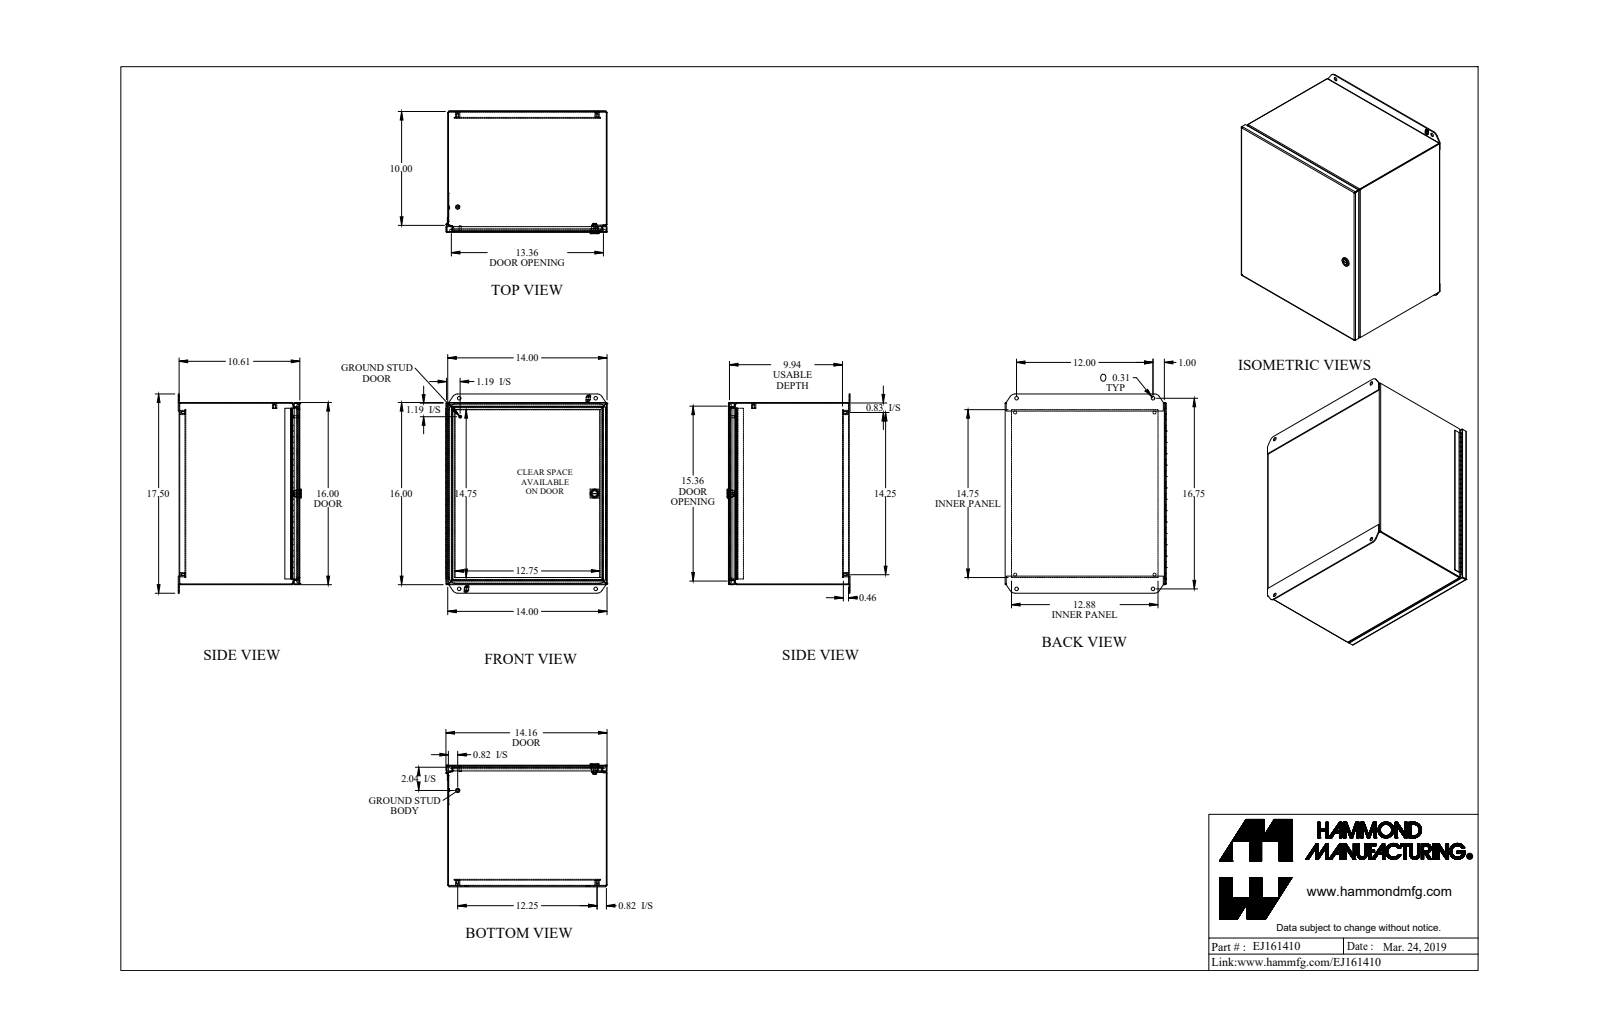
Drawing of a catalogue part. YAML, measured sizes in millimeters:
part_name: "EJ161410_Default"
step_written_by: "SolidWorks 2019 (CONFIG_CONTROL_DESIGN)"
units: millimeters
bodies: {solids: 16, faces: 771, planar: 425, cylindrical: 254, other: 92}
overall_size: [444.5, 359.8, 274.4]
volume: 1416000
surface_area: 1858000
round_holes:
  - {diameter: 4, count: 5}
  - {diameter: 6.7, count: 4}
  - {diameter: 8, count: 4}
  - {diameter: 1.3, count: 1}
  - {diameter: 13.1, count: 1}
round_bosses_or_shafts:
  - {diameter: 9.5, count: 5}
  - {diameter: 20, count: 1}
  - {diameter: 13.6, count: 1}
  - {diameter: 12.6, count: 1}
  - {diameter: 11, count: 1}
  - {diameter: 6.4, count: 1}
  - {diameter: 4.8, count: 1}
  - {diameter: 2.5, count: 1}
partial_cylinders:
  - {radius: 0.7, count: 16}
  - {radius: 2.2, count: 16}
  - {radius: 7.1, count: 10}
  - {radius: 6.4, count: 4}
  - {radius: 12.7, count: 4}
  - {radius: 12.7, count: 4}
  - {radius: 1.5, count: 2}
  - {radius: 13.7, count: 2}
face_to_face_distances: [1.4, 268.1, 354.2, 405, 1.8, 15, 269.5, 266.6, 11.7, 13.1]
hole_center_spacings: [31.9, 393.7, 499.8, 362, 309.6, 181.1, 212.7, 304.8]
